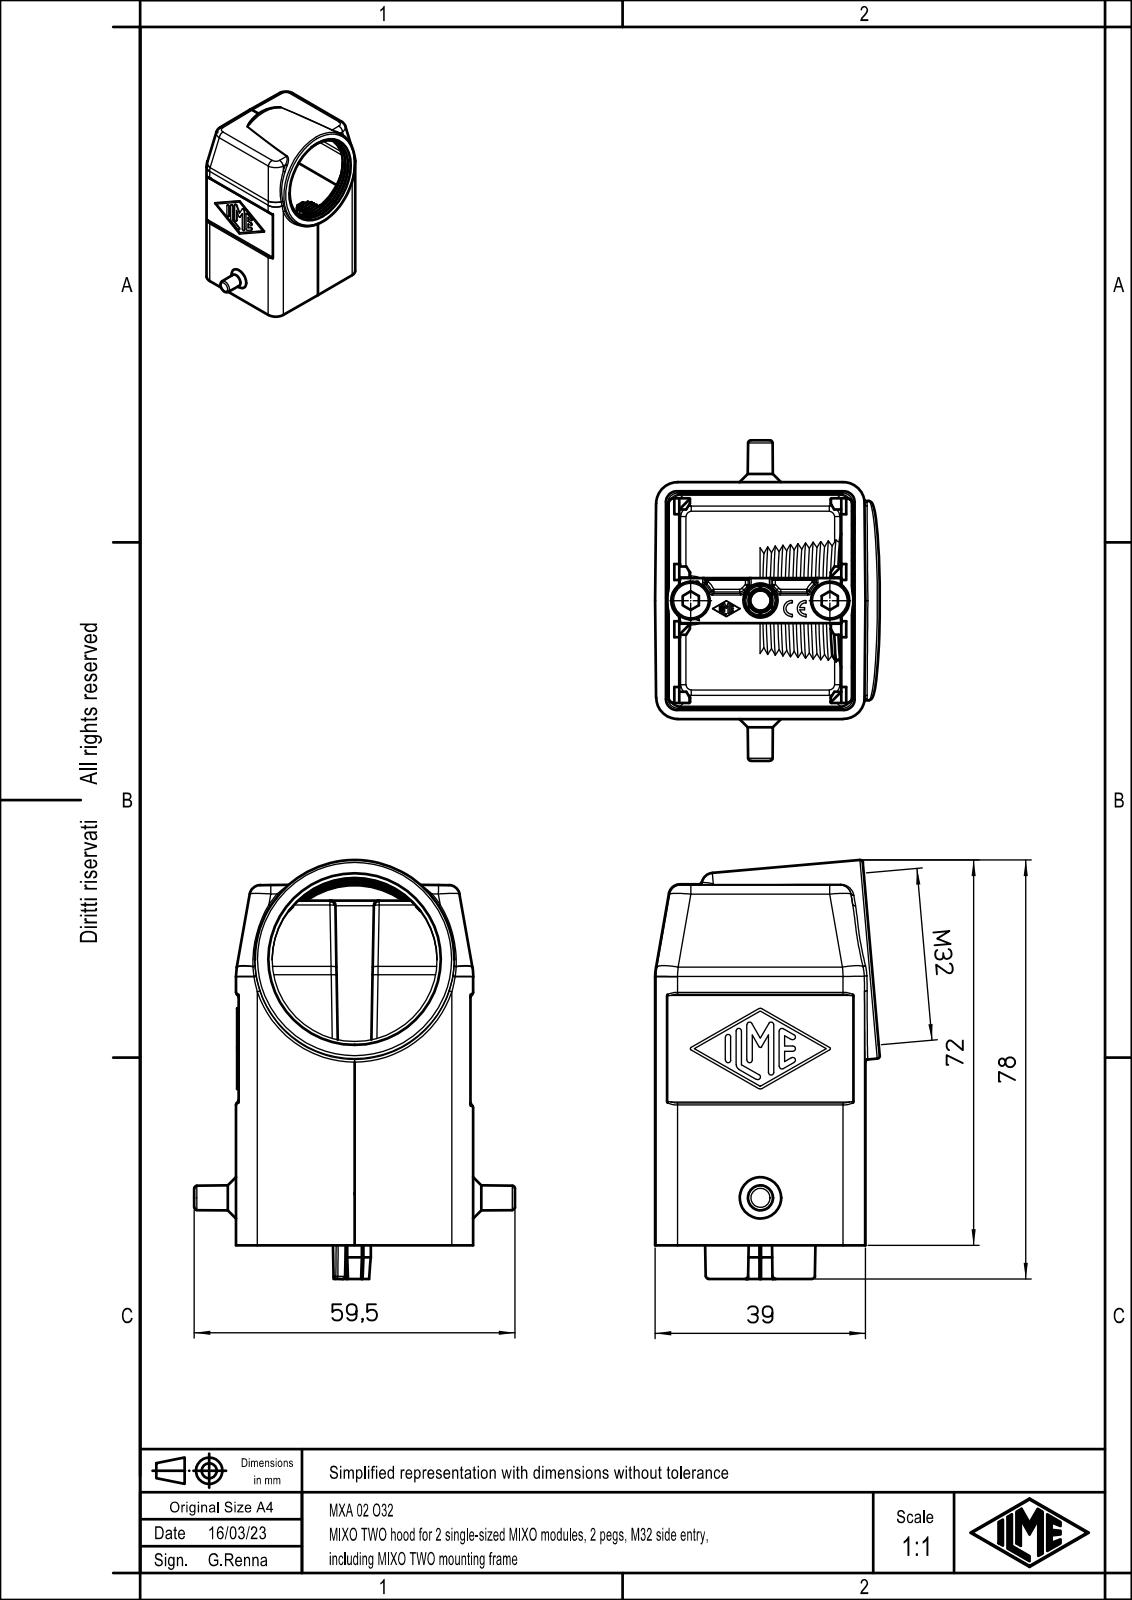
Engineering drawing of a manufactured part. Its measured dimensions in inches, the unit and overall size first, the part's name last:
Units: inches
Overall size (bounding box): 3.062 × 2.343 × 1.641
Round holes (diameter × count): ⌀0.165 ×3, ⌀0.118 ×1
Round bosses / shafts (diameter × count): ⌀0.276 ×2, ⌀1.457 ×1, ⌀0.236 ×1, ⌀0.157 ×1, ⌀0.142 ×1, ⌀0.107 ×1
Partial cylindrical surfaces — rounded edges, fillets, slot ends (radius × count): R0.004 ×45, R0.02 ×38, R0.039 ×32, R0.012 ×27, R0.008 ×15, R0.079 ×15, R0.059 ×12, R0.394 ×10
Main face-to-face distances: 1.535, 0.02, 1.713, 1.732, 0.087, 1.693, 0.907, 1.339, 0.079, 0.329
Hole centre spacings: 0.508, 0.213, 0.295, 0.803, 1.016
Volume: 1.91 in³ · Surface area: 46.83 in²
Bodies: 1 solid, 1451 faces (612 planar, 299 cylindrical, 540 other)
Part name (STEP PRODUCT): MXA 02 O32
STEP written by: Creo Elements/Direct Modeling 20.1B 02-Apr-2019 (C) Parametric Technology GmbH (AUTOMOTIVE_DESIGN)
